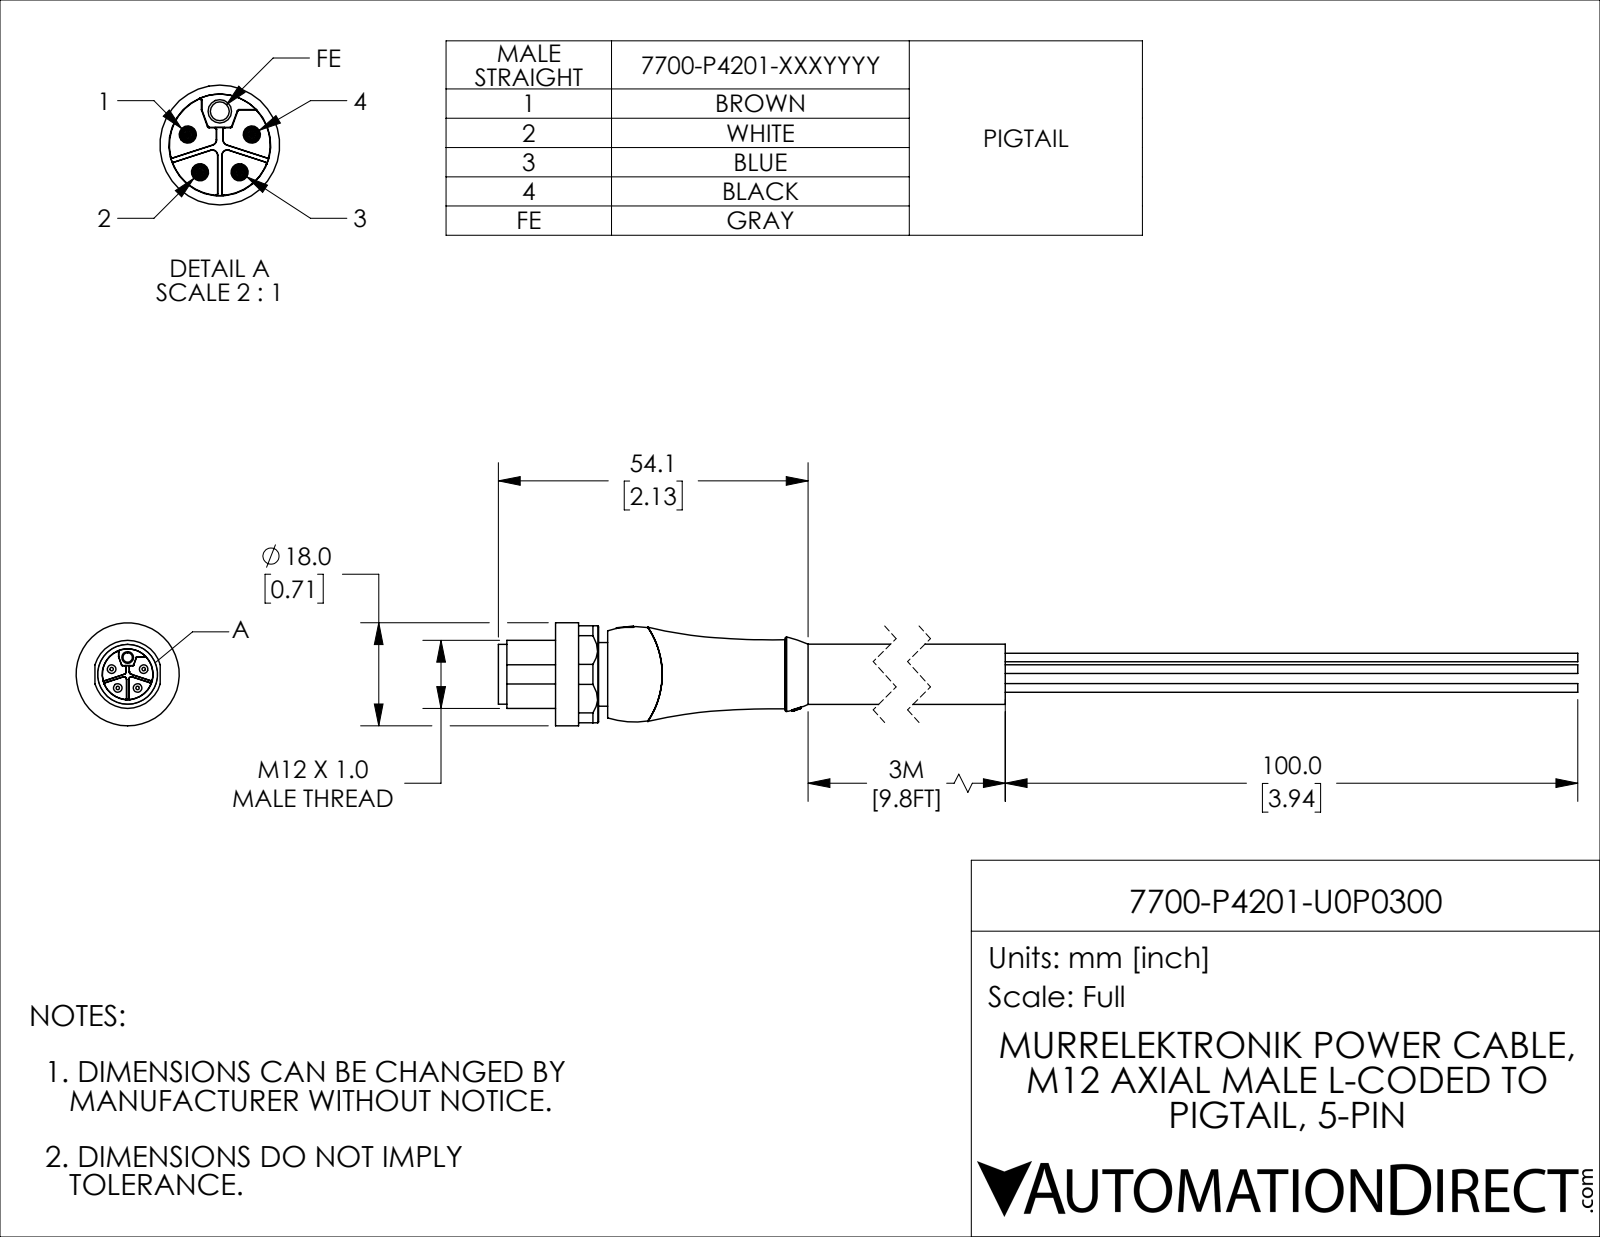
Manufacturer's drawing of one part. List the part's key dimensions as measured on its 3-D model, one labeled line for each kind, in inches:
Part name (STEP PRODUCT): 7700-P4201-U0P0300
STEP written by: SolidWorks 2021 (CONFIG_CONTROL_DESIGN)
Units: inches
Bodies: 1 solid, 190 faces (87 planar, 51 cylindrical, 52 other)
Overall size (bounding box): 10.004 × 0.709 × 0.709
Volume: 1.067 in³ · Surface area: 14.12 in²
Round holes (diameter × count): ⌀0.065 ×1
Round bosses / shafts (diameter × count): ⌀0.059 ×5, ⌀0.709 ×1, ⌀0.468 ×1, ⌀0.437 ×1, ⌀0.413 ×1, ⌀0.411 ×1
Partial cylindrical surfaces — rounded edges, fillets, slot ends (radius × count): R0.006 ×6, R0.044 ×1, R0.352 ×1
Main face-to-face distances: 0.358, 0.075, 0.283, 5.673, 5.39, 5.315, 0.667, 0.047, 0.331, 0.406
